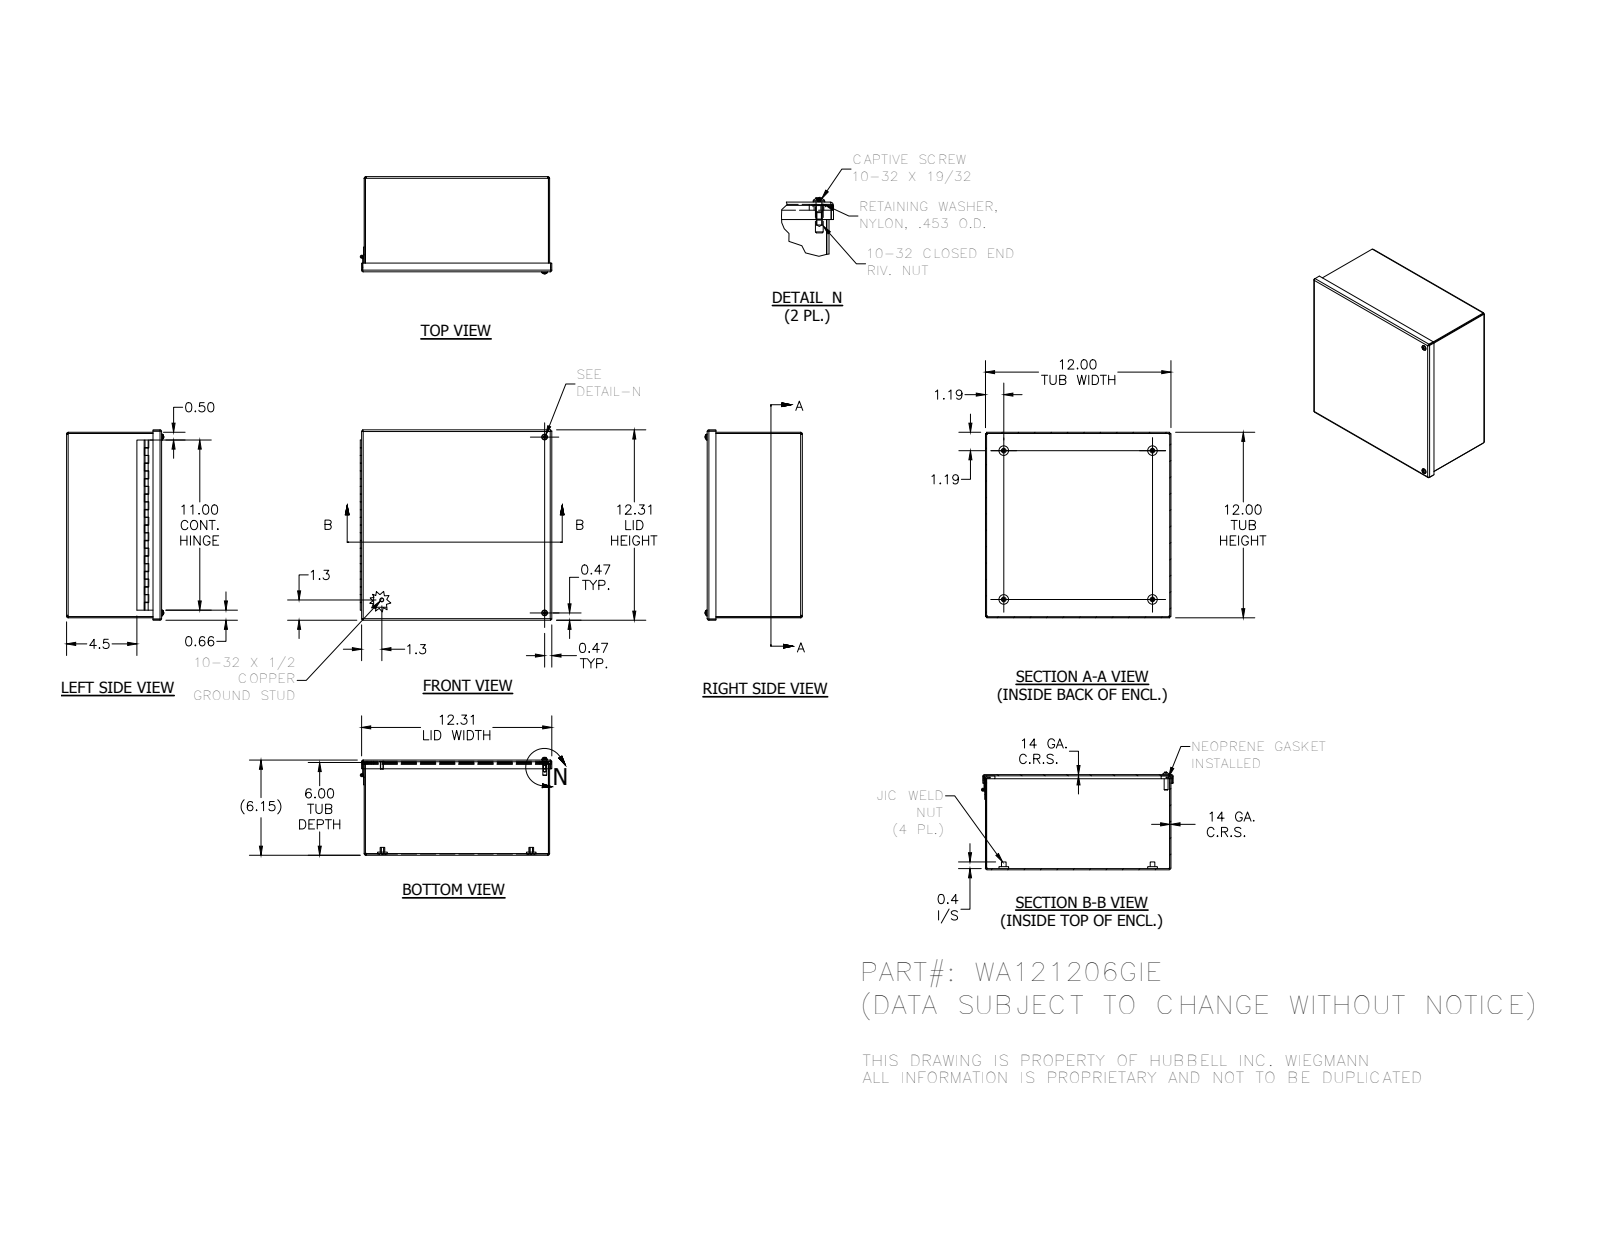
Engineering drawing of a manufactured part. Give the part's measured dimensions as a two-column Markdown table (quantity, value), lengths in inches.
| quantity | value |
| --- | --- |
| part name | WA121206GIEBKP; 3499; 328123LH; 328123P (+8 more) |
| STEP written by | Autodesk Inventor 2014 (AUTOMOTIVE_DESIGN) |
| units | inches |
| bodies | 18 solids, 485 faces (281 planar, 129 cylindrical, 75 other) |
| overall size | 12.397 × 12.313 × 6.282 |
| volume | 52.58 in³ |
| surface area | 1 368 in² |
| round holes (diameter × count) | 0.156 × 6, 0.257 × 4, 0.313 × 4, 0.196 × 2, 0.278 × 2, 0.281 × 2, 0.117 × 1 |
| round bosses / shafts (diameter × count) | 0.625 × 4, 0.3 × 4, 0.19 × 3, 0.453 × 2, 0.406 × 2, 0.373 × 2, 0.248 × 2, 0.25 × 1 |
| partial cylindrical surfaces (radius × count) | 0.031 × 12, 0.105 × 12, 0.07 × 8, 0.089 × 2 |
| main face-to-face distances | 0.074, 6.078, 11.926, 6.004, 6.152, 12, 11.852, 0.187, 0.261, 5.891 |
| hole center spacings | 11.375, 10.536, 1.237, 16.086, 9.625, 11.374, 11.386, 14.849 |
